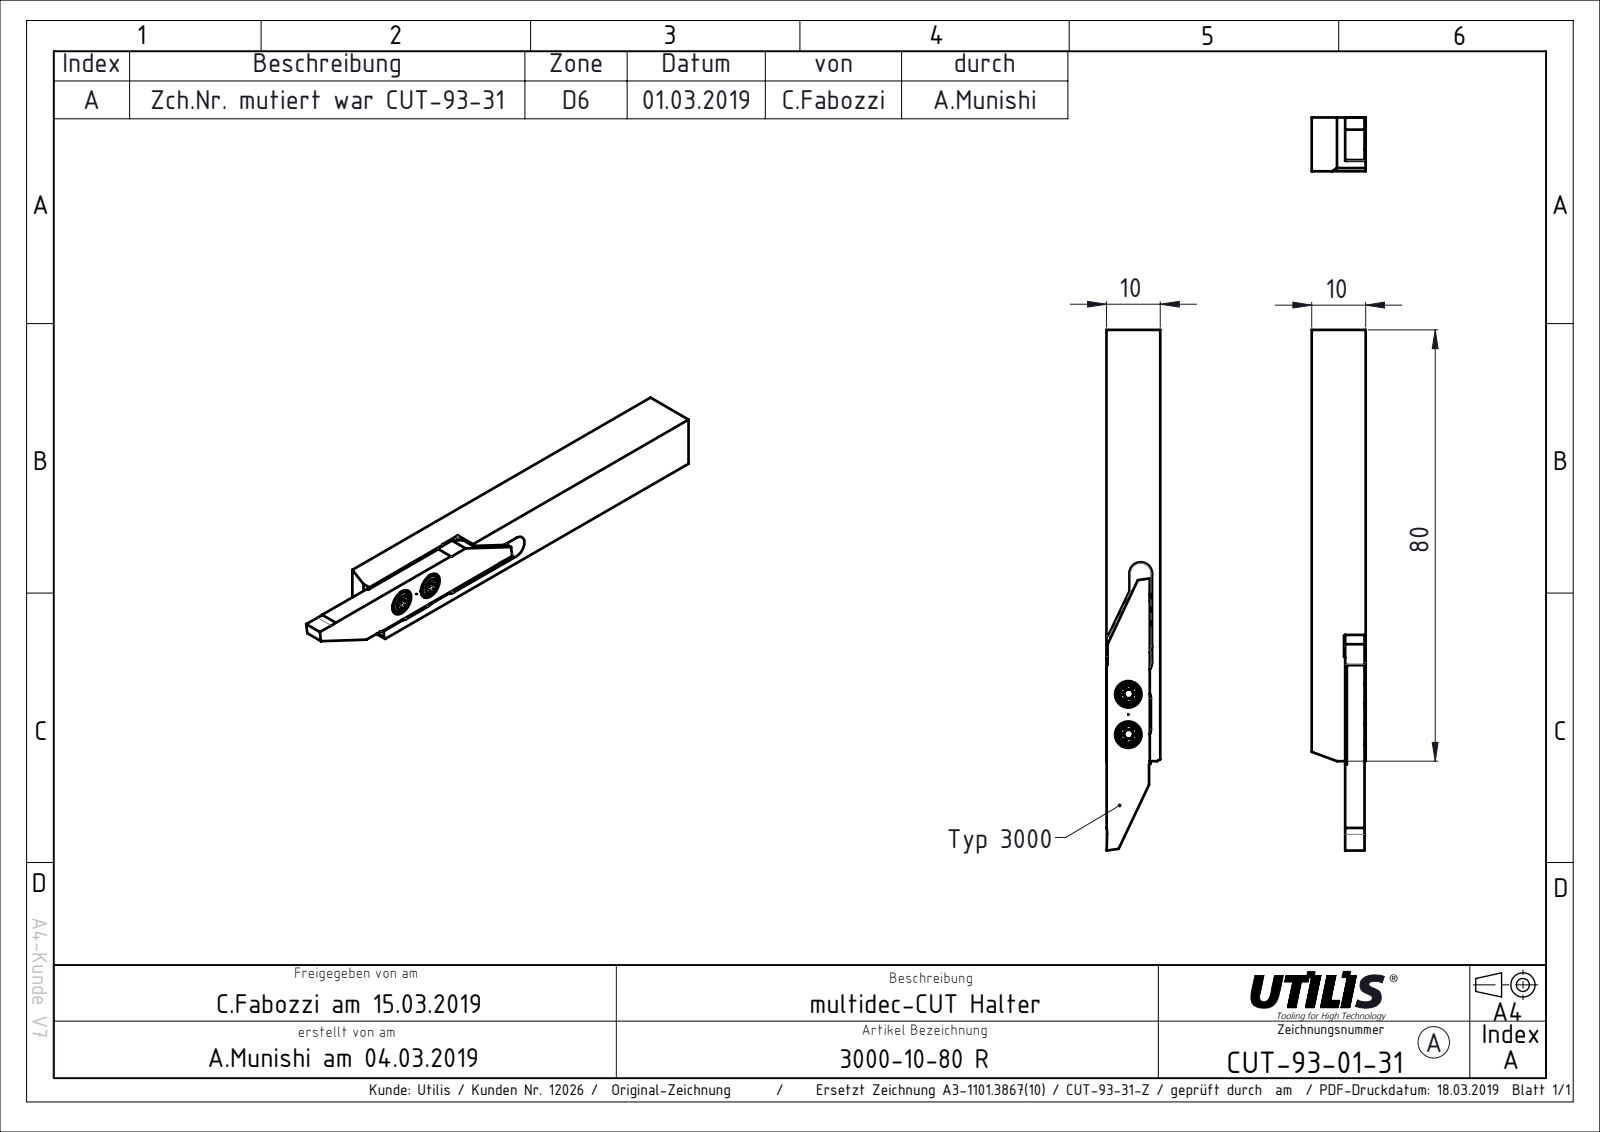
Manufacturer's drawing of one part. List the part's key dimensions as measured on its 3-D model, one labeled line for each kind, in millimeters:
Part name (STEP PRODUCT): CUT-93-31
STEP written by: SolidWorks 2016 (AUTOMOTIVE_DESIGN)
Units: millimetres
Bodies: 1 solid, 45 faces (36 planar, 9 cylindrical, 0 other)
Overall size (bounding box): 96.5 × 10 × 10
Volume: 8 139 mm³ · Surface area: 4 054 mm²
Partial cylindrical surfaces — rounded edges, fillets, slot ends (radius × count): R2.1 ×4, R0.15 ×2, R10 ×2
Main face-to-face distances: 10, 9.8, 3.6, 3.8, 6.2, 2, 8, 1.55, 0.45, 8.45
